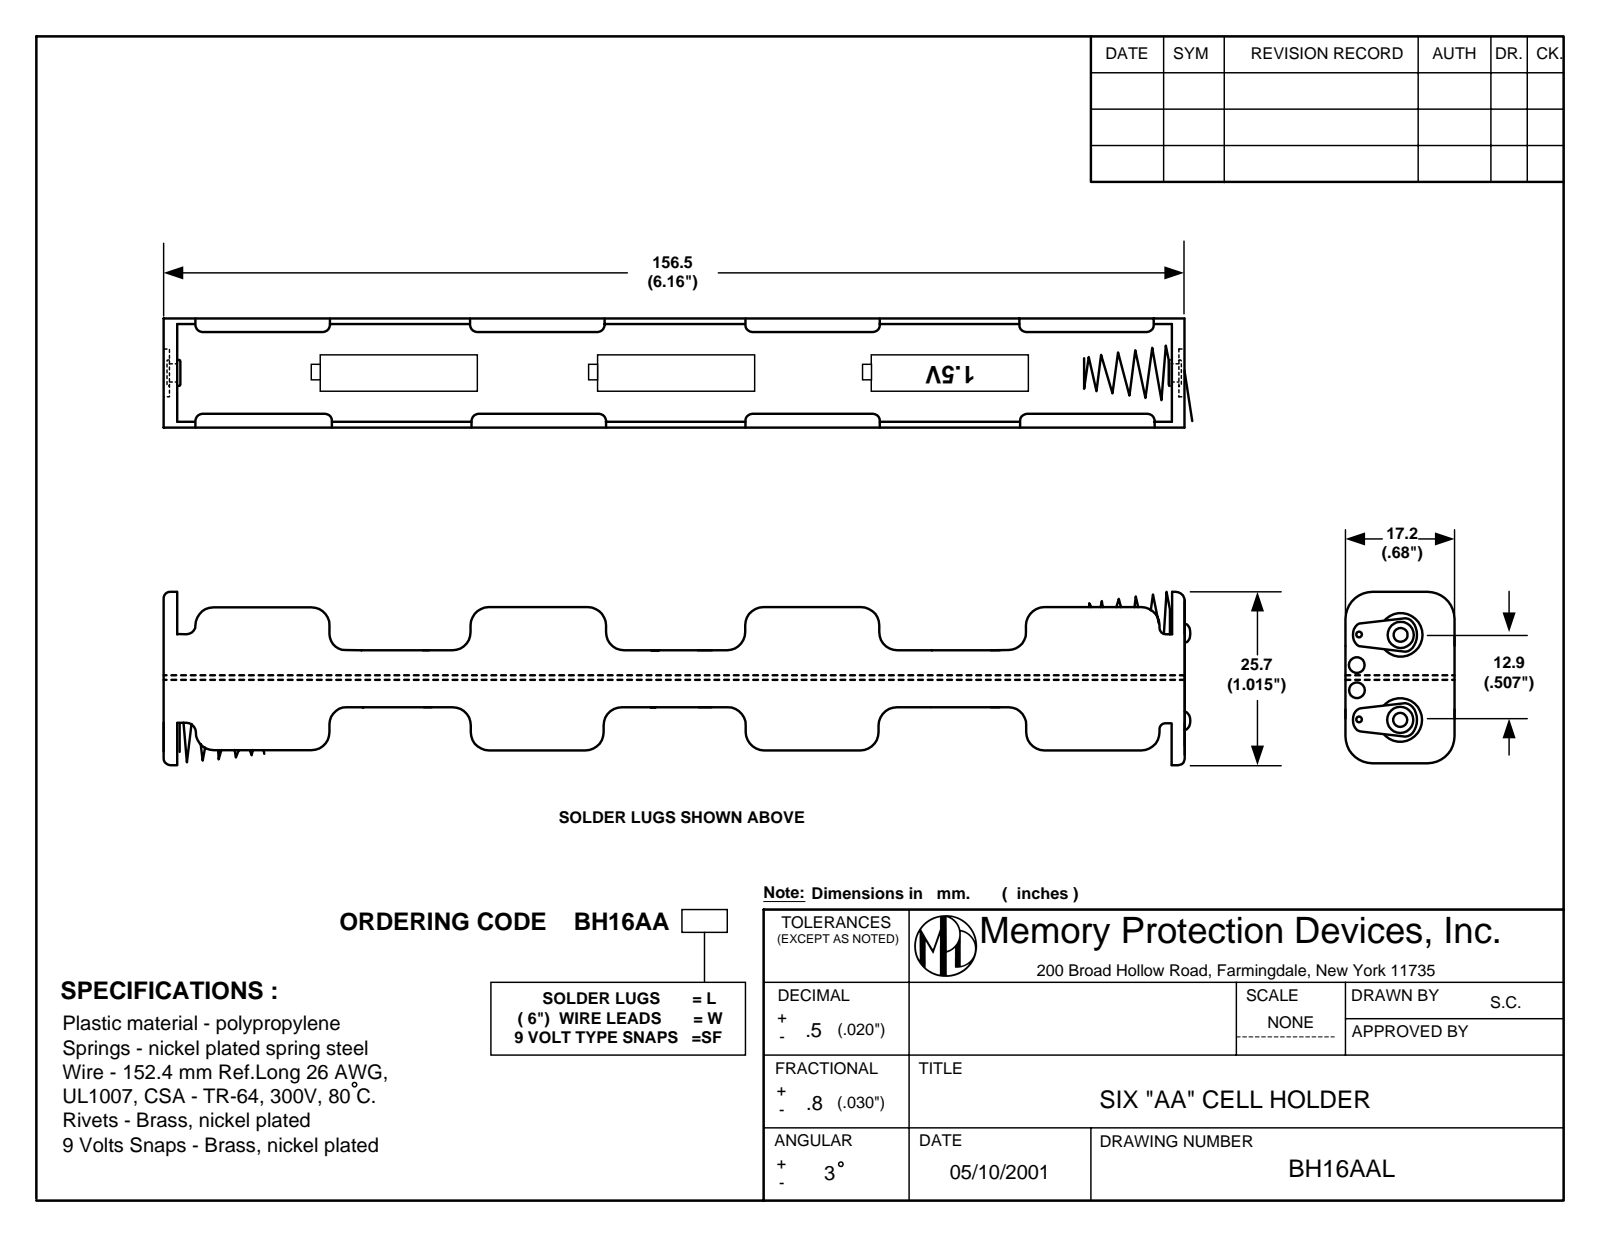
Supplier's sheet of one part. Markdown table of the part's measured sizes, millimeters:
| quantity | value |
| --- | --- |
| part name | BH16AAL |
| STEP written by | SolidWorks 2017 (AUTOMOTIVE_DESIGN) |
| units | millimeters |
| bodies | 5 solids, 610 faces (162 planar, 258 cylindrical, 190 other) |
| overall size | 158.9 × 25.7 × 17.2 |
| volume | 10 898 mm³ |
| surface area | 19 051 mm² |
| round holes (diameter × count) | 1.02 × 2, 1.6 × 2, 2.3 × 2, 2.54 × 2, 9.5 × 2 |
| round bosses / shafts (diameter × count) | 7 × 2, 6.2 × 2, 3.8 × 2, 0.63 × 2 |
| partial cylindrical surfaces (radius × count) | 0.25 × 40, 1.91 × 34, 2.5 × 4, 6.17 × 4, 9.5 × 4, 3.65 × 2, 6 × 1, 6.31 × 1 |
| main face-to-face distances | 1.3, 15.9, 17.2, 14.6, 155.2, 153.9, 0.31, 156.19, 0.99, 154.89 |
| hole center spacings | 7.42, 10.15, 12.5, 3.84 |
